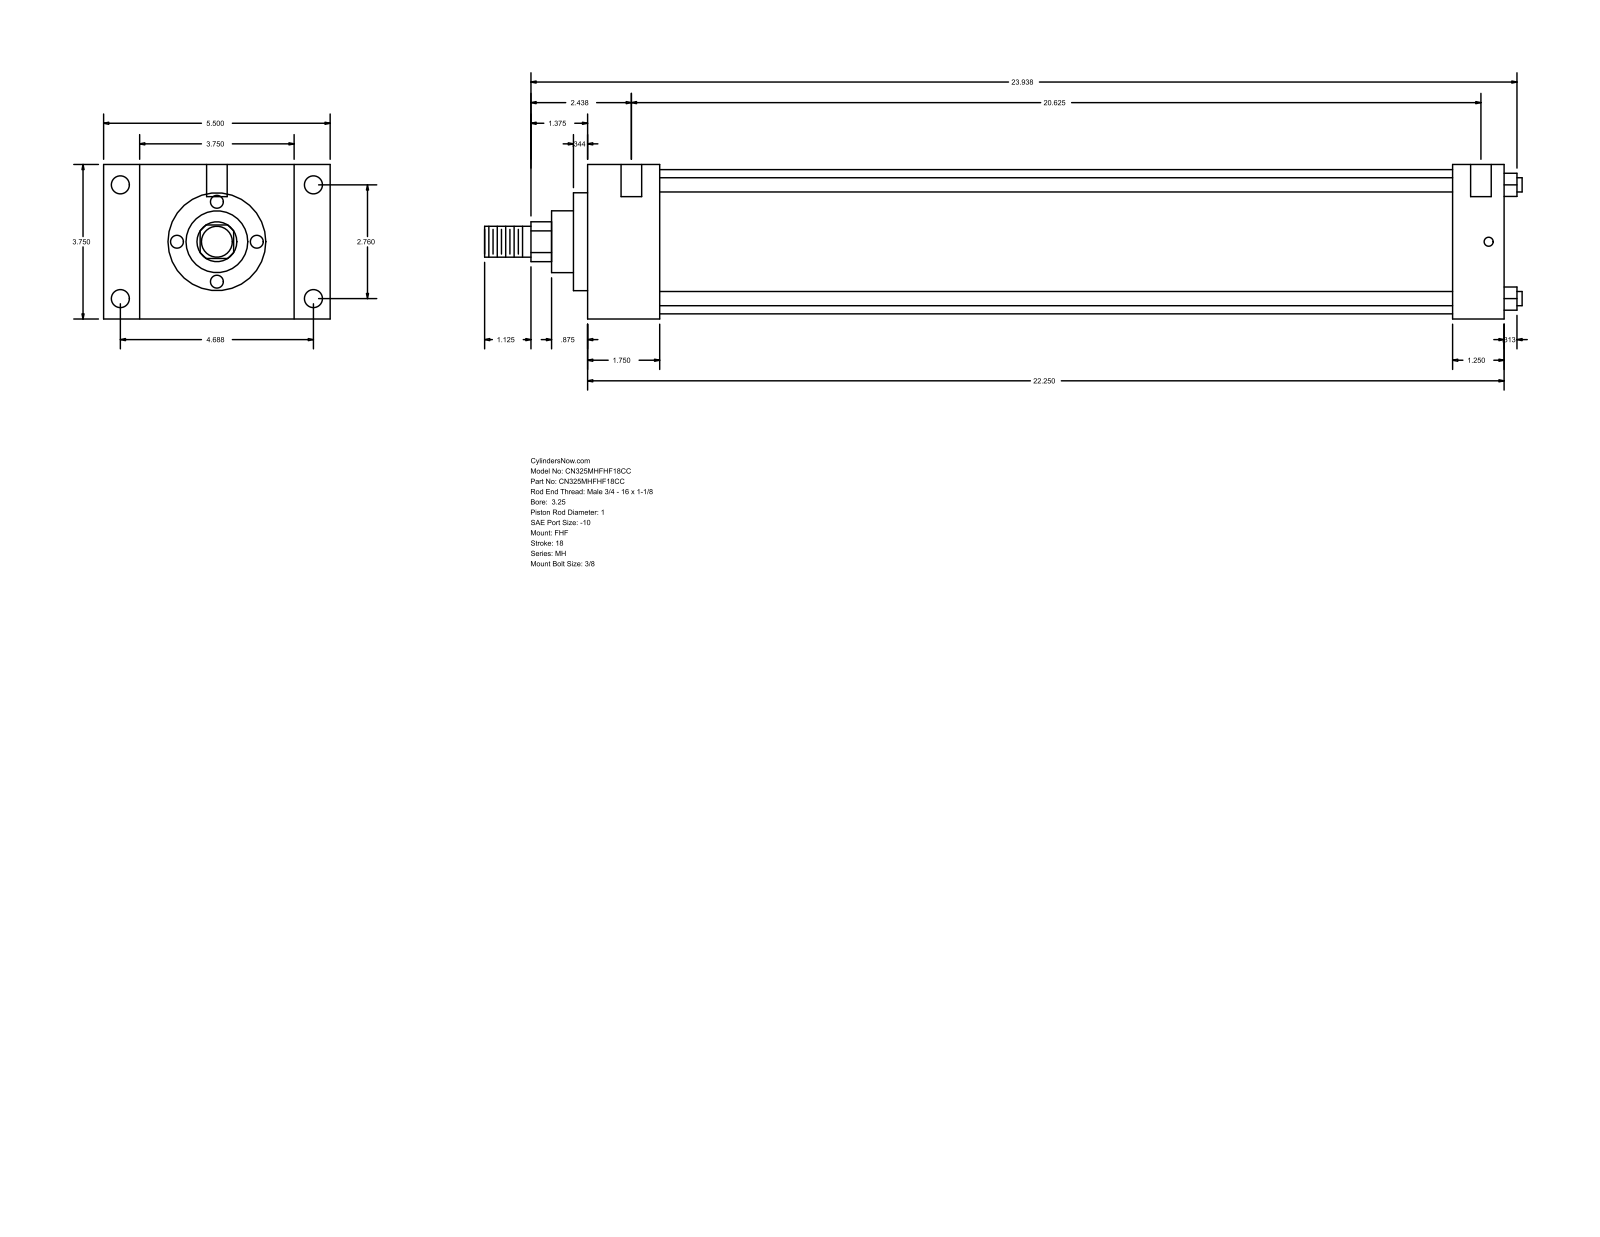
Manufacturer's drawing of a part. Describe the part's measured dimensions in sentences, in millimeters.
The part is named "MH_FHF__0325_1". Its 3-D file was written by "GSSL Pune (CONFIG_CONTROL_DESIGN)". It is 0 solids with 90 faces: 61 planar, 29 cylindrical and 0 other. Overall it measures 639.76 by 139.7 by 95.25 millimeters. Round holes: 4 of diameter 5.56, 4 of diameter 11.13, 2 of diameter 12.7. Round bosses or shafts: 4 of diameter 8.76, 1 of diameter 88.9, 1 of diameter 60.33, 1 of diameter 38.1, 1 of diameter 25.4, 1 of diameter 19.05. Partial cylindrical surfaces (rounded edges, fillets, slot ends): 1 of radius 12.29. The main face-to-face distances are 95.24, 565.16, 44.46, 520.7, 22.23, 117.47, 139.7, 533.41, 488.95, 31.75. The hole center spacings are 70.1, 119.06, 138.16, 530.22, 1.58, 4.76, 523.88, 525.46.
